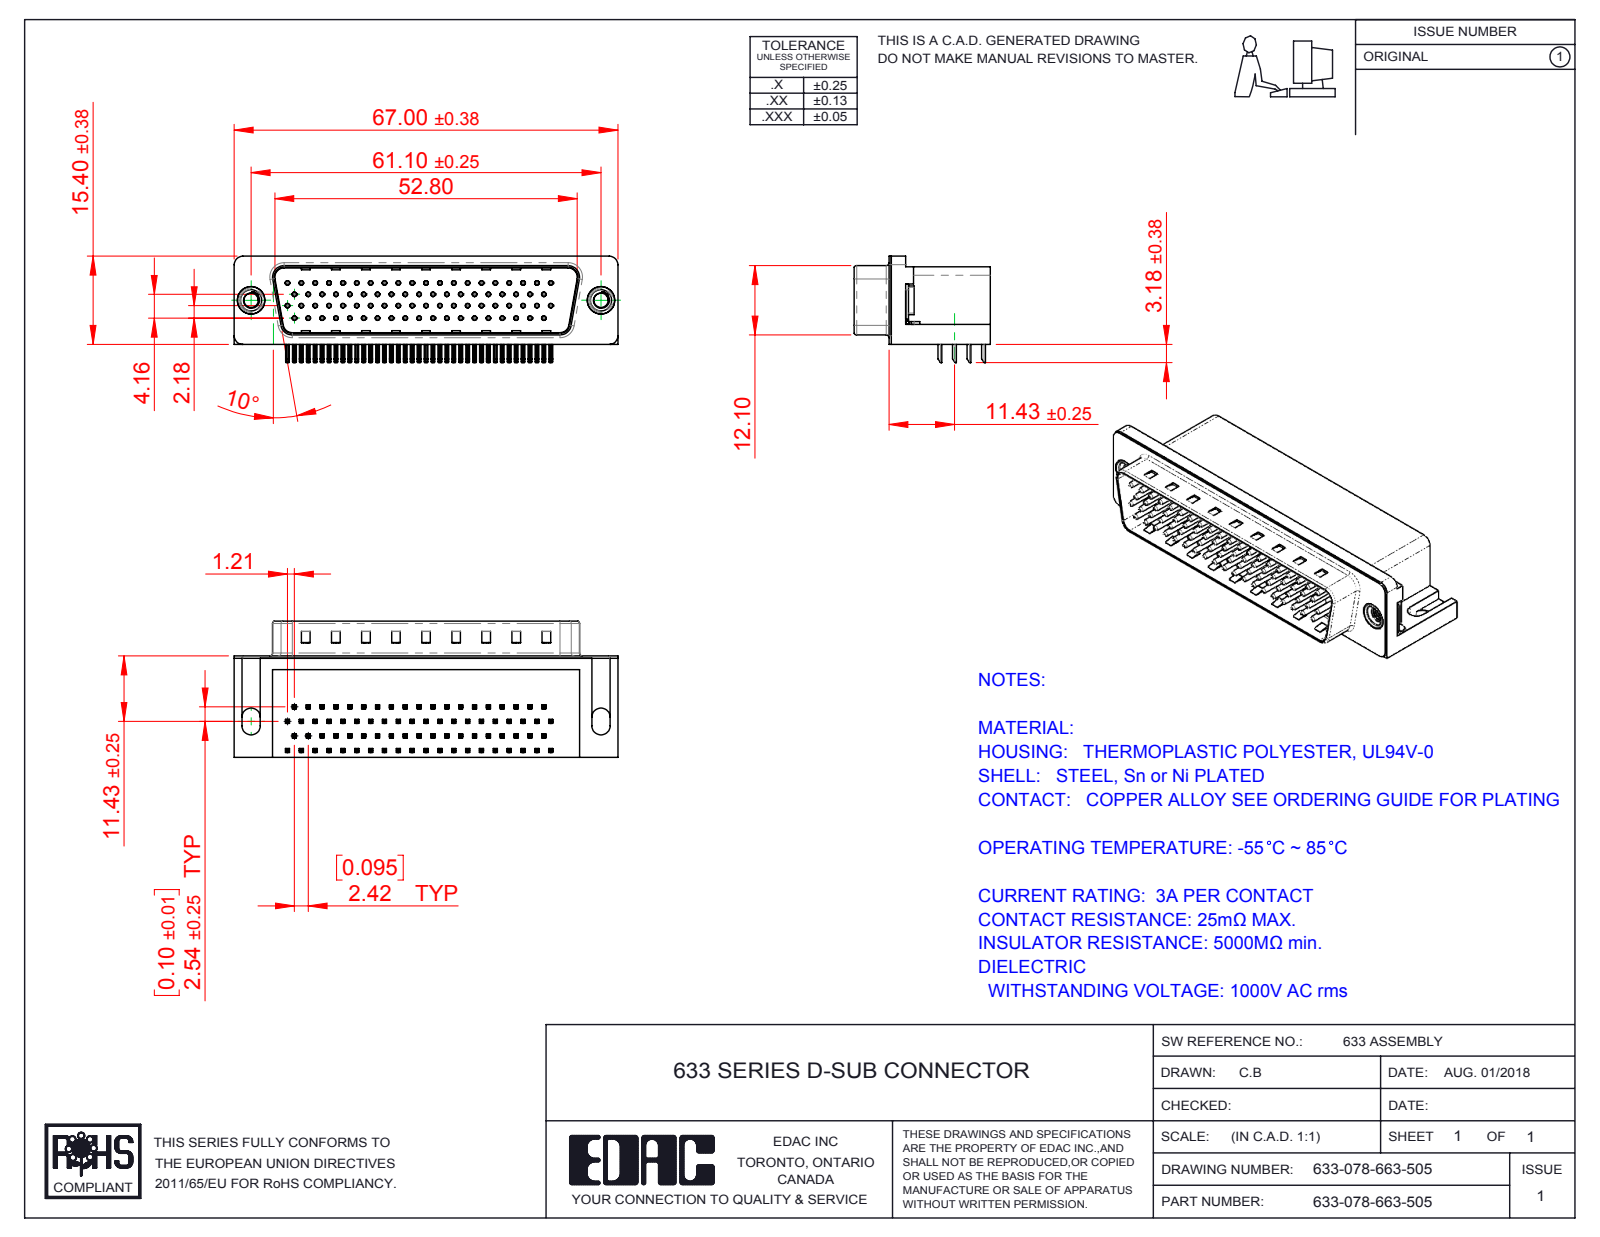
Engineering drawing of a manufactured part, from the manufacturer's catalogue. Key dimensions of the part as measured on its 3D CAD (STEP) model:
Part name (STEP PRODUCT): 633 Housing_78 Contact; 633 M3 Threaded Rivet; 633 Non Board Mount_78 Contact; 633 Shell_78 Contact (+5 more)
STEP written by: SolidWorks 2016 (CONFIG_CONTROL_DESIGN)
Units: millimetres
Bodies: 84 solids, 6270 faces (3979 planar, 1778 cylindrical, 513 other)
Overall size (bounding box): 67 × 23.8 × 18.58
Volume: 14 559 mm³ · Surface area: 16 128 mm²
Round holes (diameter × count): ⌀0.35 ×78, ⌀0.8 ×78, ⌀2.5 ×2, ⌀4 ×2, ⌀4.8 ×2, ⌀5 ×2
Round bosses / shafts (diameter × count): ⌀0.75 ×78, ⌀4.9 ×2, ⌀4.75 ×2, ⌀3.9 ×2
Partial cylindrical surfaces — rounded edges, fillets, slot ends (radius × count): R0.25 ×320, R0.12 ×156, R1 ×16, R0.5 ×9, R1.6 ×8, R1.5 ×6, R0.45 ×4, R0.9 ×4
Main face-to-face distances: 0.4, 13.2, 17.3, 11.7, 13.35, 2.05, 13.75, 1.65, 11.9, 1.85
Hole centre spacings: 2.42, 4.84, 7.26, 9.68, 6.26, 7.13, 12.1, 8.62
